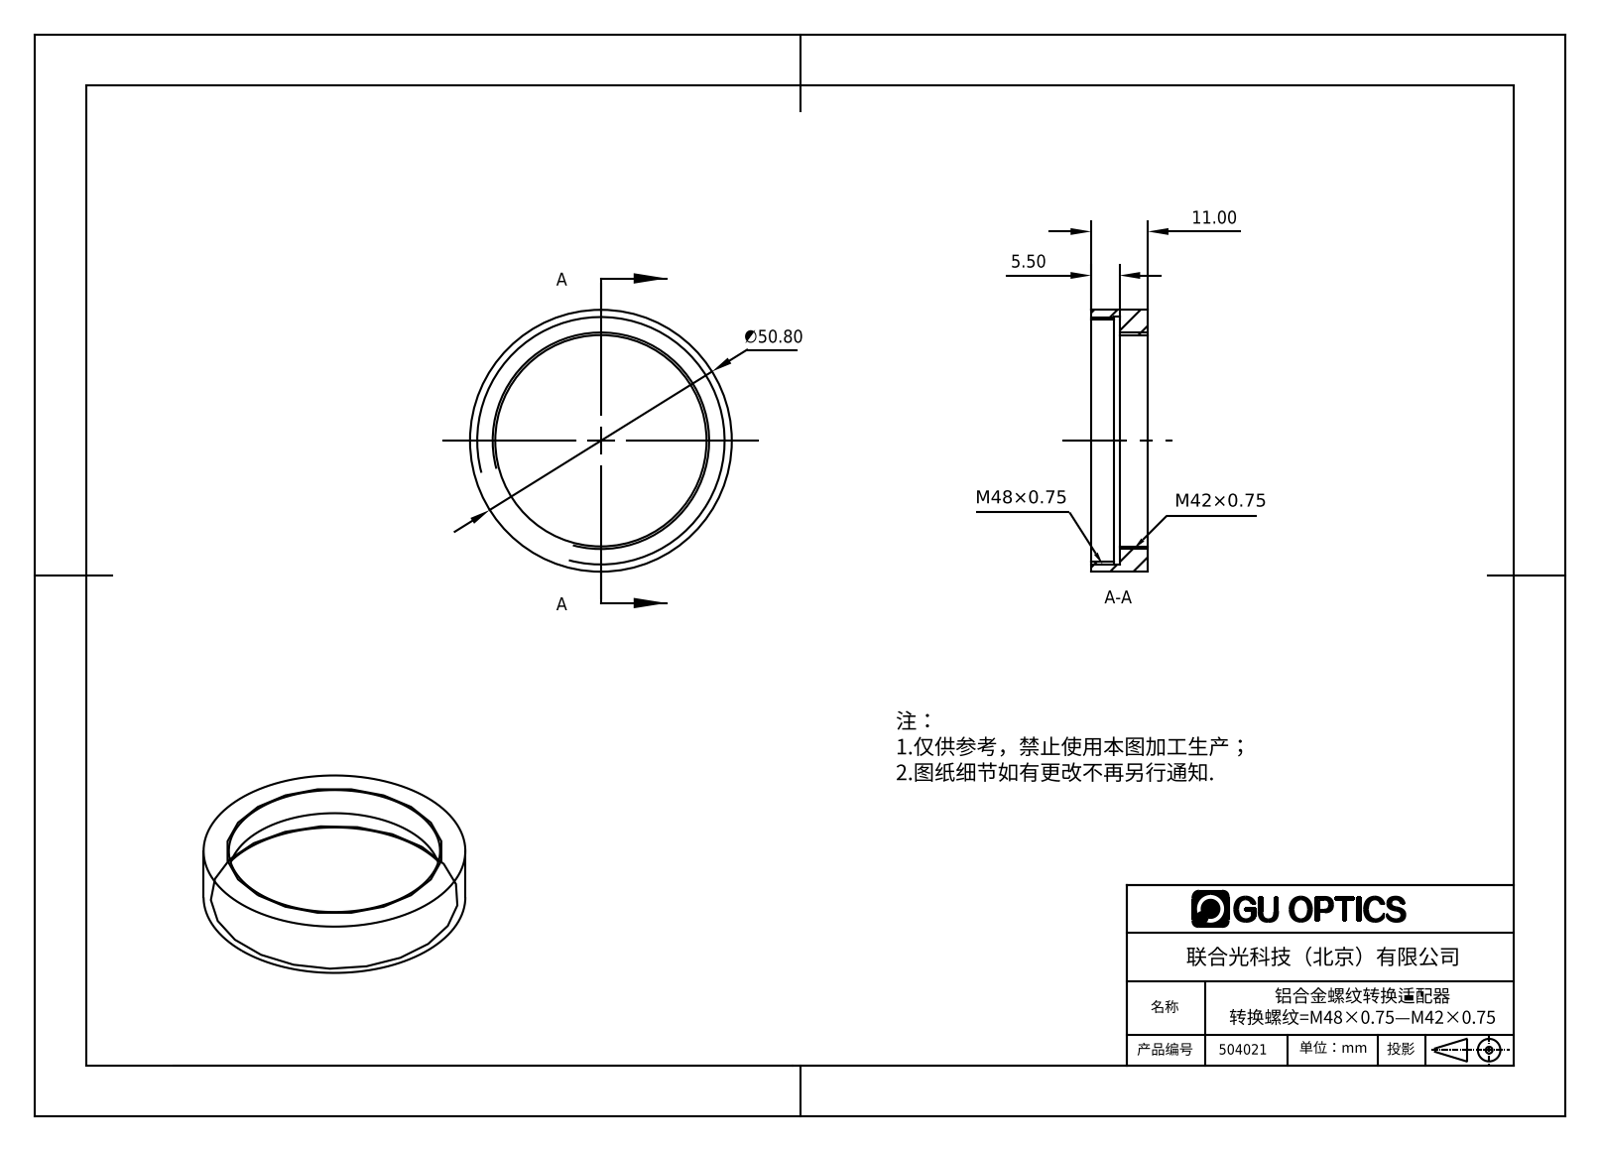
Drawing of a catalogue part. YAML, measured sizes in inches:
part_name: "504021"
step_written_by: "SolidWorks 2016 (AUTOMOTIVE_DESIGN)"
units: inches
bodies: {solids: 1, faces: 12, planar: 4, cylindrical: 8, other: 0}
overall_size: [2, 2, 0.433]
volume: 0.33
surface_area: 7.552
round_holes:
  - {diameter: 1.614, count: 1}
  - {diameter: 1.85, count: 1}
  - {diameter: 1.898, count: 1}
round_bosses_or_shafts:
  - {diameter: 2, count: 1}
face_to_face_distances: [0.217, 0.433, 0.177, 0.039, 0.256]
